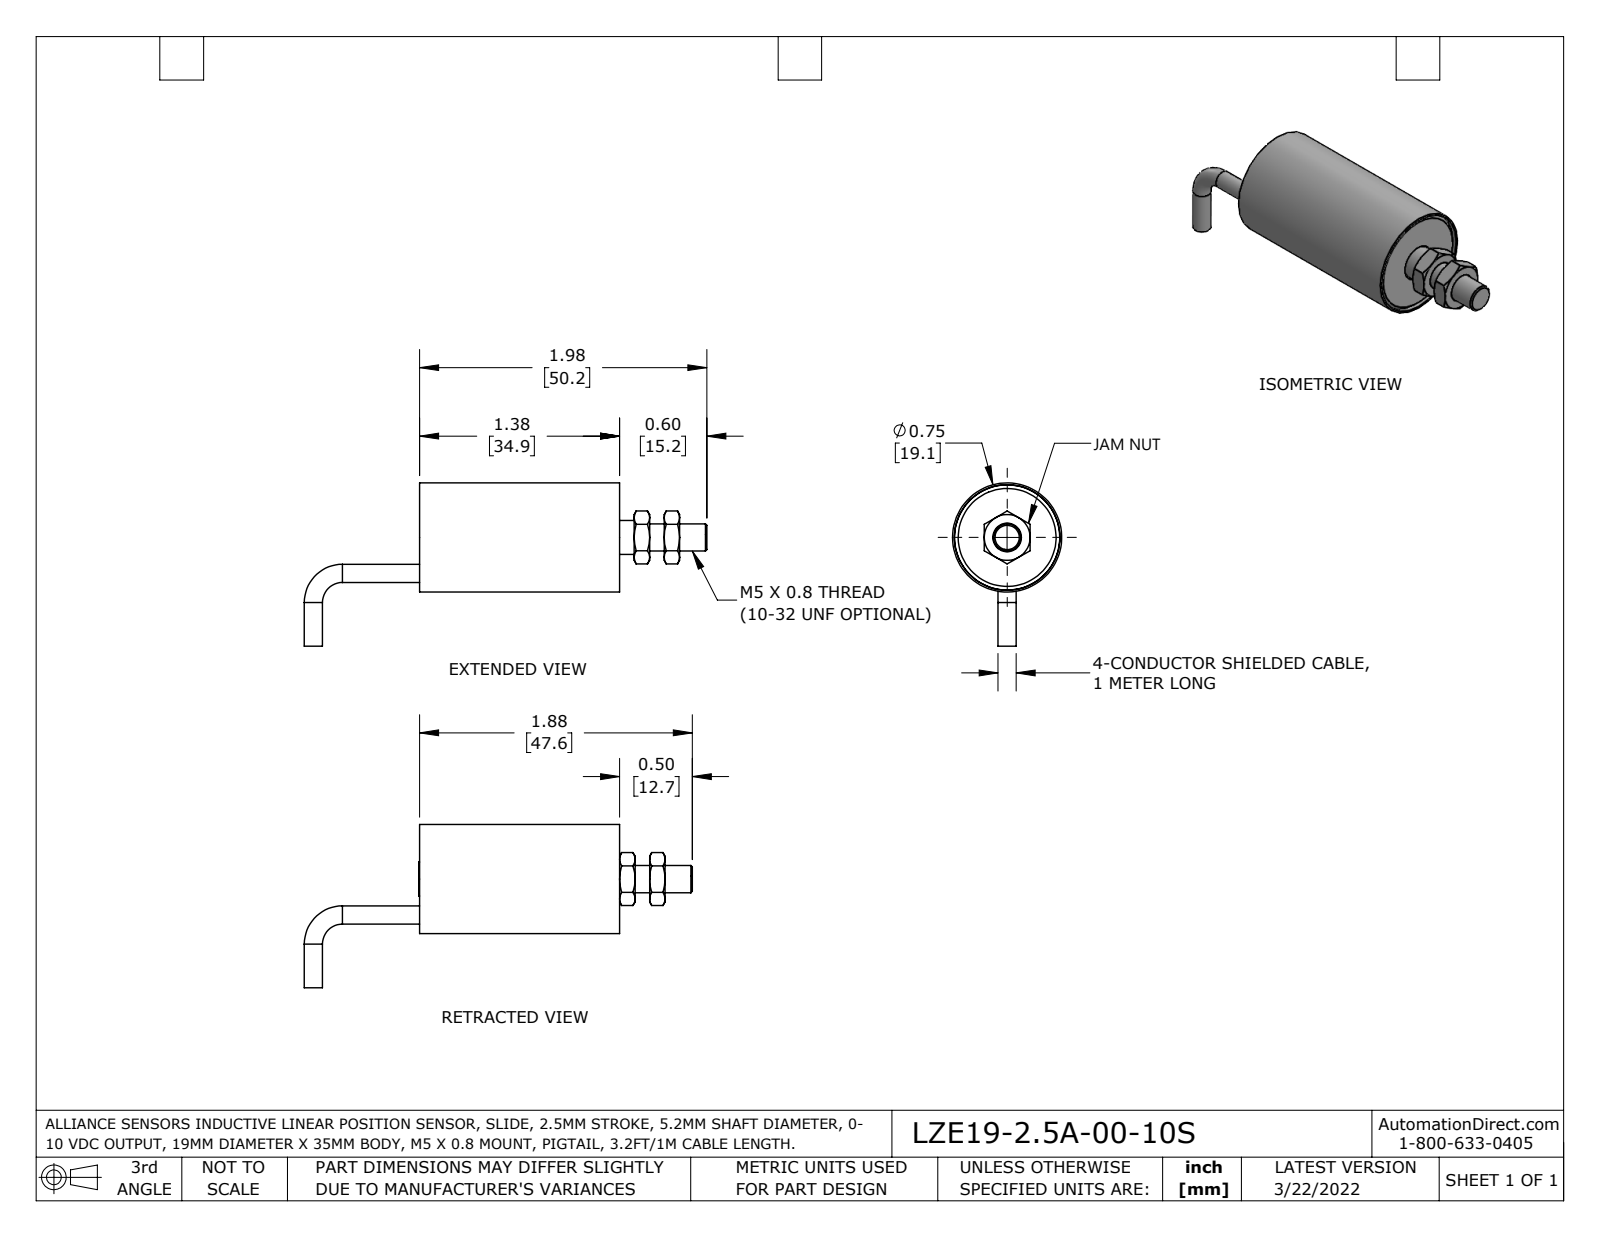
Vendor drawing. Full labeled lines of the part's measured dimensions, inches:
Part name (STEP PRODUCT): 3120-0008-06_-01; 5500-0031; 3120-0007-ZY_with slot; LZE19-2.5A-00-10S (+6 more)
STEP written by: SolidWorks 2021 (AUTOMOTIVE_DESIGN)
Units: inches
Bodies: 10 solids, 137 faces (42 planar, 44 cylindrical, 51 other)
Overall size (bounding box): 2.768 × 1.121 × 0.75
Volume: 0.3 in³ · Surface area: 15.45 in²
Round holes (diameter × count): ⌀0.165 ×1, ⌀0.188 ×1, ⌀0.197 ×1, ⌀0.234 ×1, ⌀0.281 ×1, ⌀0.68 ×1, ⌀0.725 ×1
Round bosses / shafts (diameter × count): ⌀0.125 ×2, ⌀0.75 ×1, ⌀0.723 ×1, ⌀0.278 ×1, ⌀0.187 ×1
Partial cylindrical surfaces — rounded edges, fillets, slot ends (radius × count): R0.052 ×1
Main face-to-face distances: 0.06, 1.295, 0.08, 1.235, 1.355, 0.206, 0.315, 0.1, 0.106, 0.374
